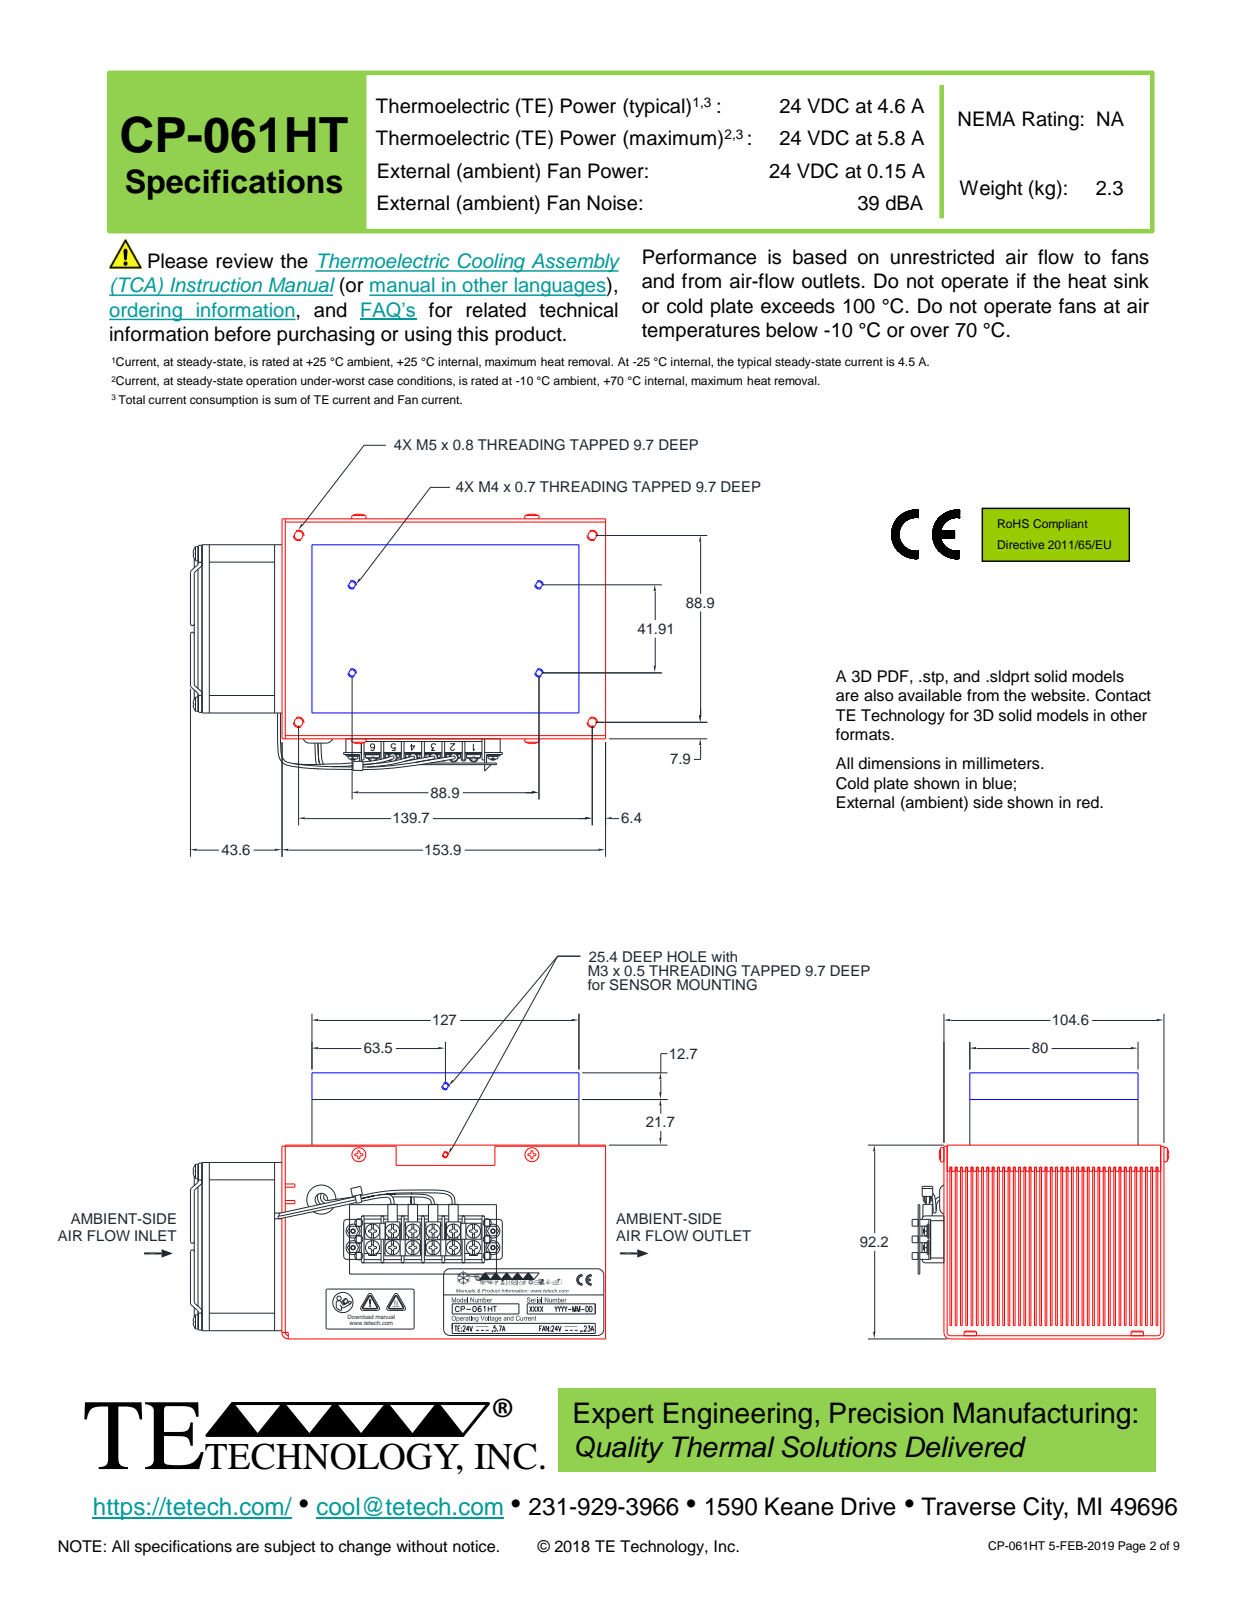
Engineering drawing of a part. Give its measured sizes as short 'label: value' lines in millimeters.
name: 4728 heat sink assy; 4771 heat sink shroud; PEM CLSS-M5-2; PEM LKS 6-32-2 (+8 more)
written by: Alibre (AUTOMOTIVE_DESIGN)
unit: mm
bodies: 154 solids, 3407 faces (2053 planar, 551 cylindrical, 803 other)
size: 197.5 × 126.8 × 122.4
volume: 993 700 mm³; area: 1 012 000 mm²
holes: 17× ⌀2.6, 8× ⌀4.1, 7× ⌀5.6, 6× ⌀4.3, 4× ⌀1.7, 4× ⌀1.9, 4× ⌀2.2, 4× ⌀2.4, 4× ⌀2.6, 4× ⌀3.3, 4× ⌀3.5, 4× ⌀3.9
bosses: 21× ⌀3.5, 18× ⌀6.9, 15× ⌀1.8, 11× ⌀1.4, 10× ⌀1.8, 4× ⌀9.5, 4× ⌀8.6, 4× ⌀7.5
rounds: 21× R1, 16× R0.8, 8× R0.4, 8× R0.8, 8× R0.8, 8× R0.8, 8× R2, 4× R0.2
face distances: 5, 10.1, 15.1, 2.5, 2.5, 7.5, 12.6, 7.5, 20.1, 17.6
hole spacings: 7.9, 19.1, 20.6, 9.5, 12.4, 9.4, 9.5, 12.3
